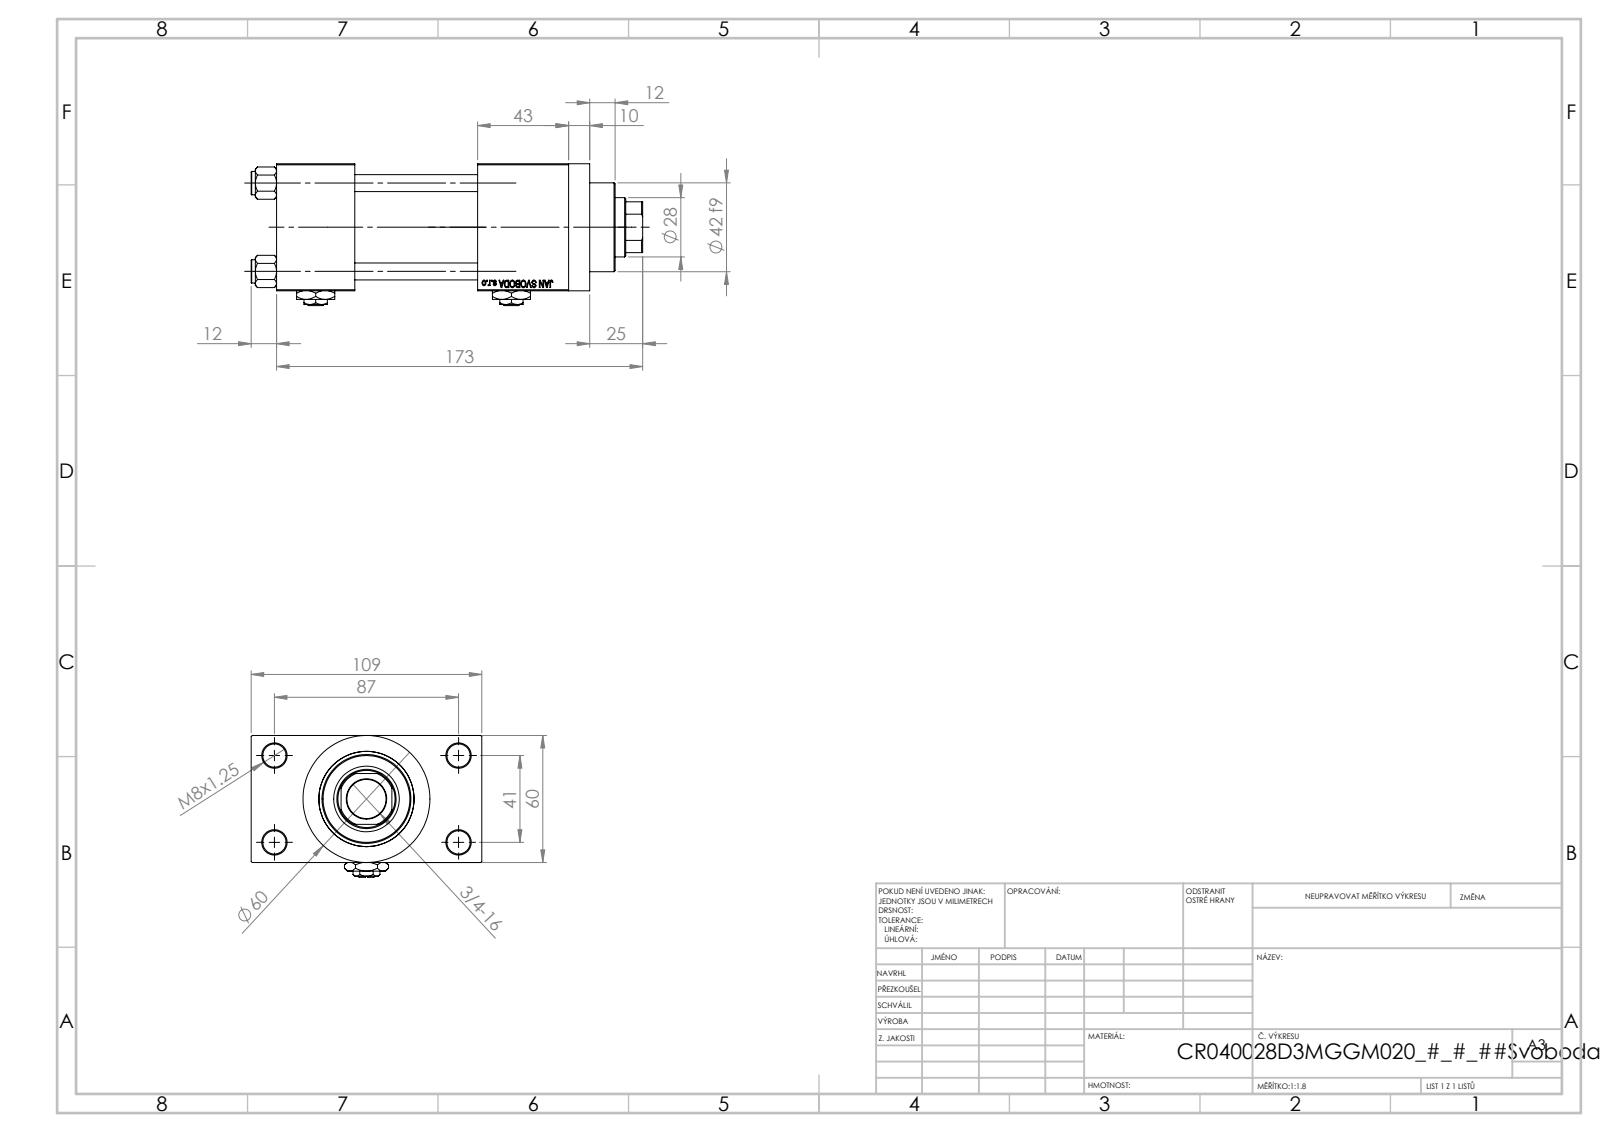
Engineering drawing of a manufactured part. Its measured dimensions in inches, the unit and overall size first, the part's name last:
Units: inches
Overall size (bounding box): 7.283 × 4.291 × 2.638
Round holes (diameter × count): ⌀0.315 ×4, ⌀0.433 ×4, ⌀0.276 ×2, ⌀0.656 ×2, ⌀0.945 ×2, ⌀0.728 ×1, ⌀1.102 ×1, ⌀1.22 ×1, ⌀1.575 ×1, ⌀1.772 ×1
Round bosses / shafts (diameter × count): ⌀0.433 ×4, ⌀2.362 ×1, ⌀1.811 ×1, ⌀1.654 ×1
Partial cylindrical surfaces — rounded edges, fillets, slot ends (radius × count): R0.531 ×1
Main face-to-face distances: 2.362, 3.327, 0.965, 2.283, 1.457, 3.74, 5.433, 3.976, 1.693, 4.291
Hole centre spacings: 0.892, 1.161, 1.642, 1.856, 1.893, 2.533, 3.011, 1.614
Volume: 32.46 in³ · Surface area: 202.2 in²
Bodies: 13 solids, 1206 faces (546 planar, 100 cylindrical, 560 other)
Part name (STEP PRODUCT): V215CR_D_TYCINKA; V215CR_D_Body; V215CR_VCP_D; Zatka_pro_OIL_PORT (+2 more)
STEP written by: SolidWorks 2019 (CONFIG_CONTROL_DESIGN)
